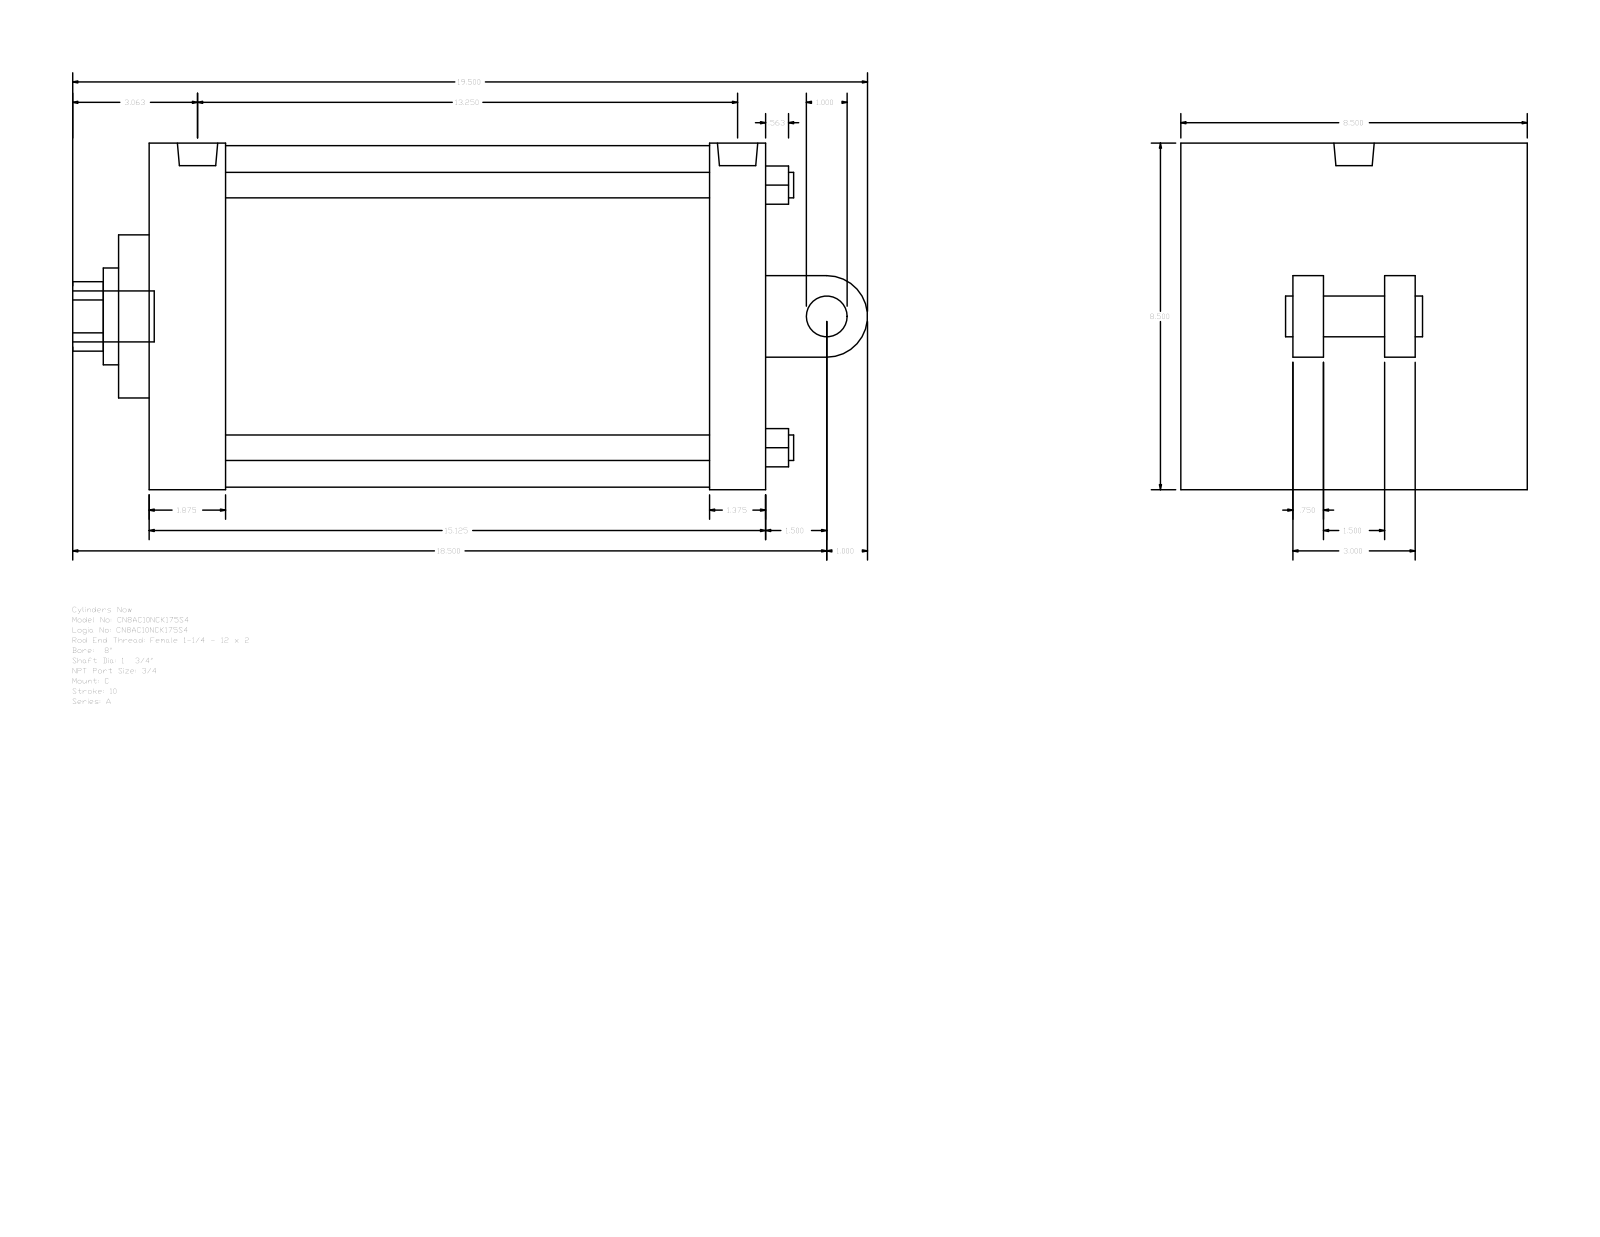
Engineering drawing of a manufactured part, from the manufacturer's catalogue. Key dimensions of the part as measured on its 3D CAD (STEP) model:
Part name (STEP PRODUCT): A_C__0800_1.75
STEP written by: GSSL Pune (CONFIG_CONTROL_DESIGN)
Units: millimetres
Bodies: 0 solids, 104 faces (75 planar, 29 cylindrical, 0 other)
Overall size (bounding box): 495.3 × 215.9 × 215.9
Round holes (diameter × count): ⌀15.88 ×4, ⌀15.08 ×2, ⌀25.12 ×1, ⌀44.45 ×1, ⌀60.33 ×1, ⌀212.72 ×1
Round bosses / shafts (diameter × count): ⌀15.08 ×2, ⌀31.75 ×1, ⌀25.4 ×1, ⌀25.12 ×1
Partial cylindrical surfaces — rounded edges, fillets, slot ends (radius × count): R21.63 ×1, R25.4 ×1
Main face-to-face distances: 384.18, 215.9, 19.05, 57.15, 34.92, 47.63, 336.55, 349.26, 301.63, 88.9
Hole centre spacings: 115.67, 163.58, 231.34, 6.35
